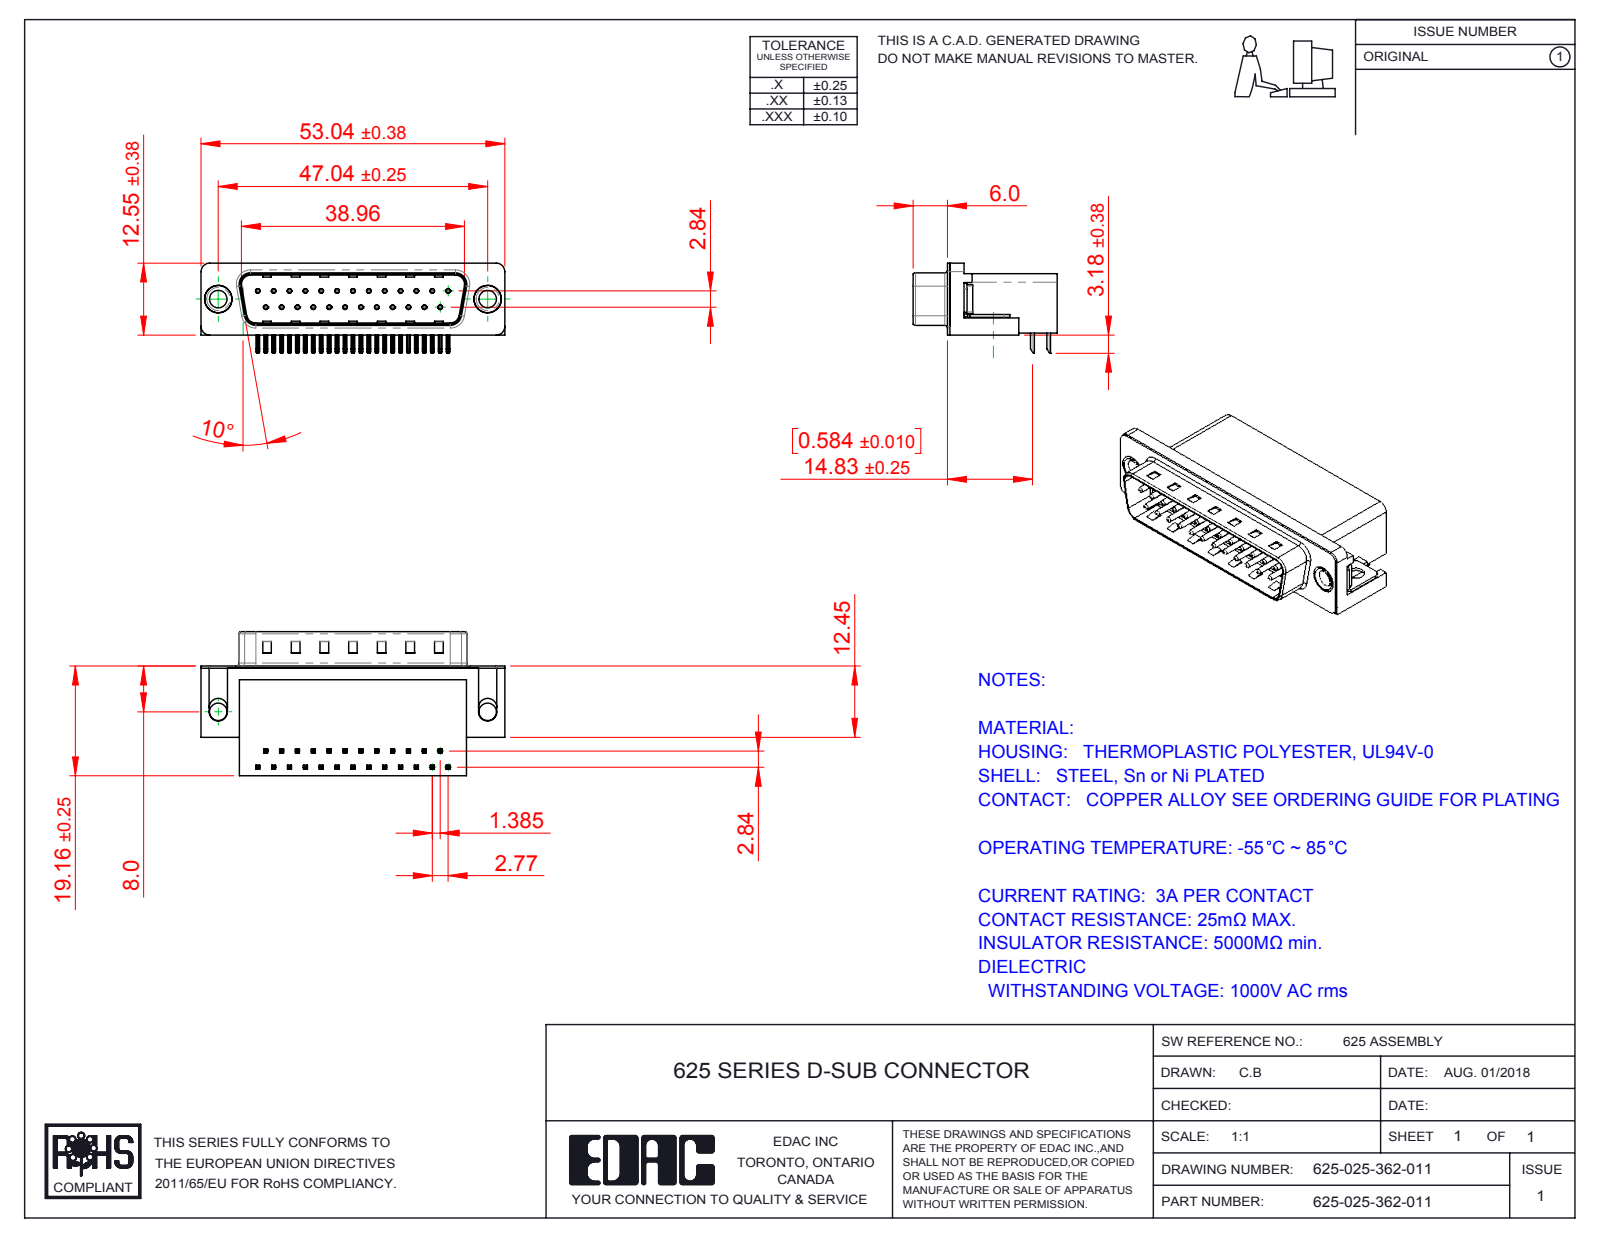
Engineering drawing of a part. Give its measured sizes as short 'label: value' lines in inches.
name: 625 Housing_25 Socket; 625 Thru Hole Rivet; 625 Contact Top; 625 Shell_25 Socket (+3 more)
written by: SolidWorks 2016 (CONFIG_CONTROL_DESIGN)
unit: in
bodies: 31 solids, 2225 faces (1405 planar, 643 cylindrical, 177 other)
size: 2.088 × 0.991 × 0.619
volume: 0.558 in³; area: 13.68 in²
holes: 25× ⌀0.014, 25× ⌀0.031, 4× ⌀0.12, 2× ⌀0.157, 2× ⌀0.189, 2× ⌀0.197
bosses: 25× ⌀0.03, 2× ⌀0.193, 2× ⌀0.187, 2× ⌀0.152
rounds: 108× R0.01, 50× R0.005, 16× R0.039, 9× R0.02, 8× R0.063, 7× R0.059, 4× R0.035, 4× R0.079
face distances: 0.016, 0.407, 0.739, 0.083, 0.345, 0.412, 0.428, 0.067, 0.754, 0.398
hole spacings: 0.124, 0.109, 0.436, 0.218, 0.327, 0.198, 0.545, 0.294
